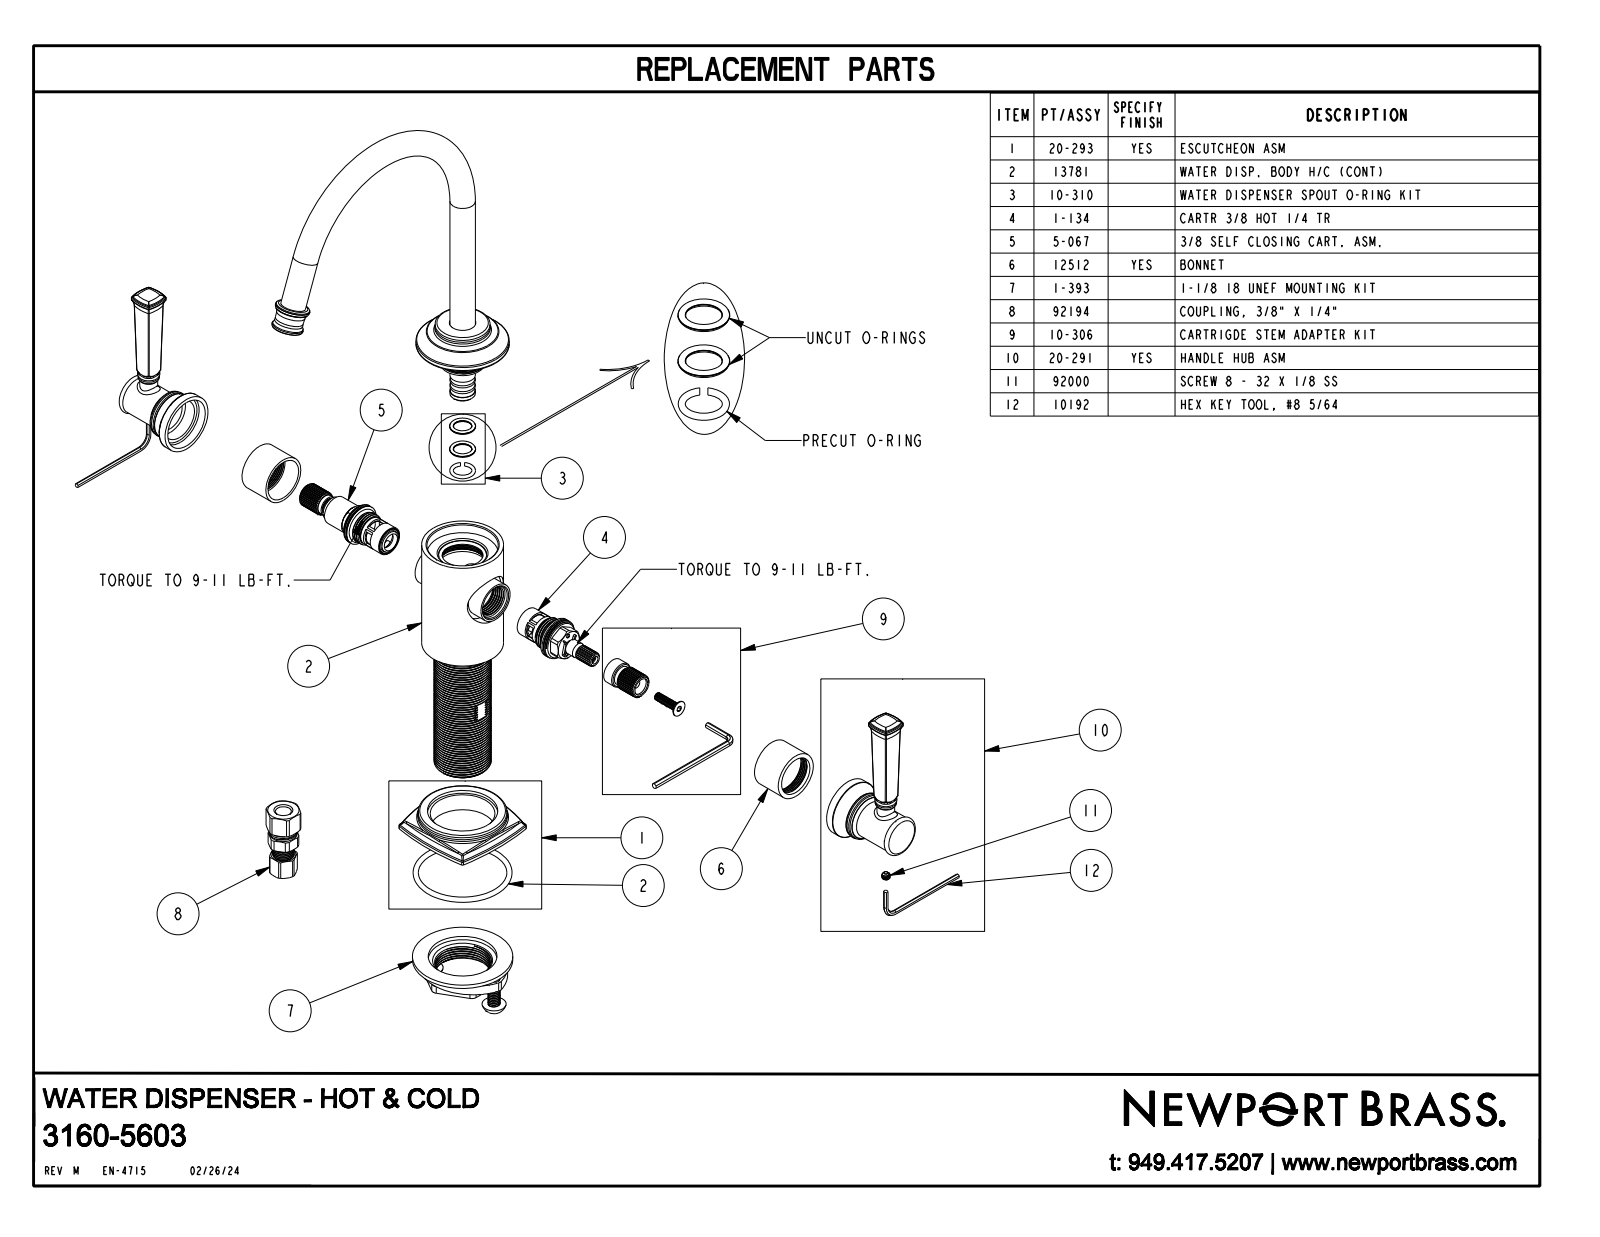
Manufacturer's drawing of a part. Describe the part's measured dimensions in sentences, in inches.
The part is named "3160-5603". Its 3-D file was written by "CREO PARAMETRIC BY PTC INC, 2018400 (CONFIG_CONTROL_DESIGN)". It is 1 solid with 394 faces: 16 planar, 56 cylindrical and 322 other. Overall it measures 9.425 by 5.993 by 5.125 inches. Its volume is 12.14 cubic inches and its surface area 61.25 square inches. Round holes: 1 of diameter 1. Round bosses or shafts: 2 of diameter 0.5, 2 of diameter 0.35, 1 of diameter 1.83, 1 of diameter 1.61, 1 of diameter 1.19, 1 of diameter 0.97, 1 of diameter 0.76. Partial cylindrical surfaces (rounded edges, fillets, slot ends): 8 of radius 0.02, 8 of radius 0.8, 4 of radius 0.03, 4 of radius 5.18, 4 of radius 5.25. The main face-to-face distances are 3.306, 2.775, 0.531, 5.125, 1.49, 3.635, 2.145, 3.635, 1.49, 4.416.
